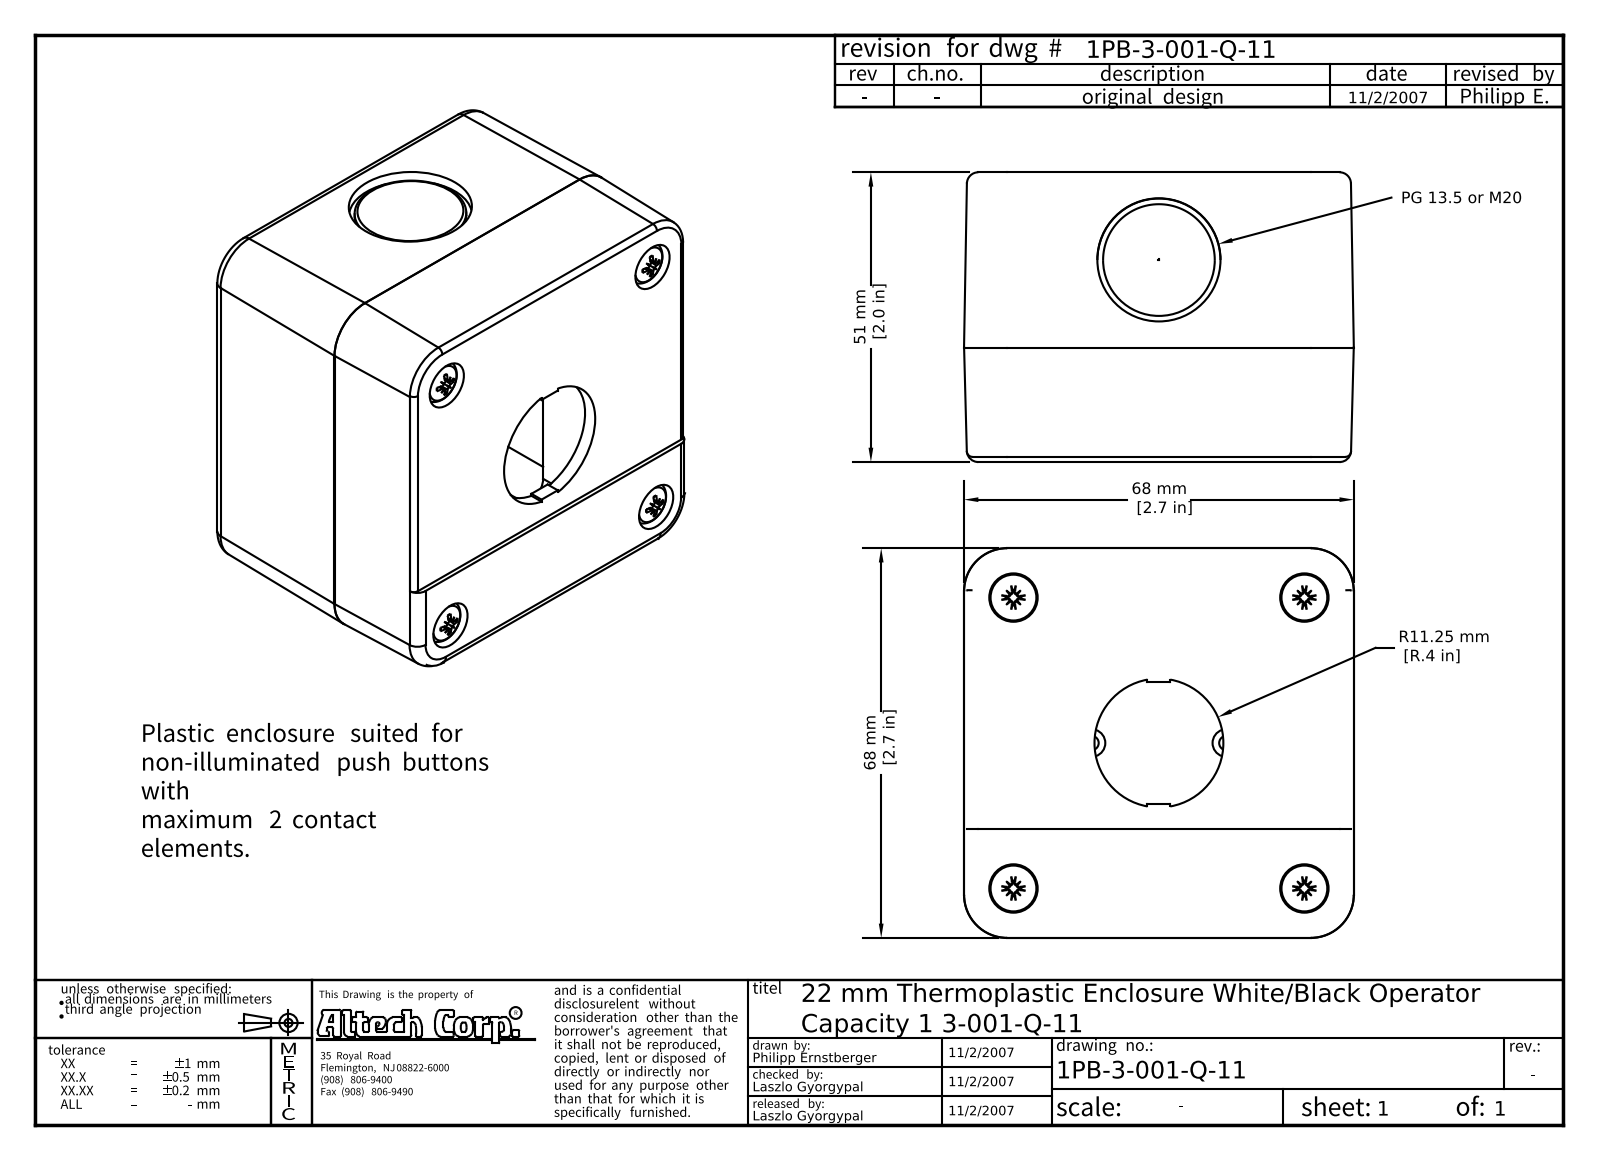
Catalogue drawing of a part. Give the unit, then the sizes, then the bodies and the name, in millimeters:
Units: millimetres
Overall size (bounding box): 68.07 × 68.07 × 50.6
Round holes (diameter × count): ⌀1.5 ×2, ⌀4.45 ×2, ⌀8.45 ×2, ⌀21.5 ×2, ⌀2.5 ×1, ⌀22.5 ×1
Round bosses / shafts (diameter × count): ⌀4 ×4, ⌀3.62 ×4, ⌀19.5 ×2, ⌀9.45 ×2, ⌀5.45 ×2, ⌀23.5 ×1, ⌀4.81 ×1, ⌀3.36 ×1
Partial cylindrical surfaces — rounded edges, fillets, slot ends (radius × count): R2 ×7, R3 ×4, R3.5 ×4, R4 ×4, R5 ×4, R6.5 ×4, R7 ×4, R7.3 ×4
Main face-to-face distances: 0.5, 2, 3.1, 49.2, 46.6, 49.7, 46.1, 0.9, 43.25, 1.5
Hole centre spacings: 6.67, 14.78, 35.92, 11.77, 13, 22.46, 28.83, 34.13
Volume: 50 959 mm³ · Surface area: 72 687 mm²
Bodies: 6 solids, 448 faces (199 planar, 79 cylindrical, 170 other)
Part name (STEP PRODUCT): 3-001-Q-11; Teknic_enclousure_back; Teknic_enclousure; NF EN ISO 7045 - Z M4 x 30 - 4.8 - Z
STEP written by: Autodesk Inventor 2008 (AUTOMOTIVE_DESIGN)
